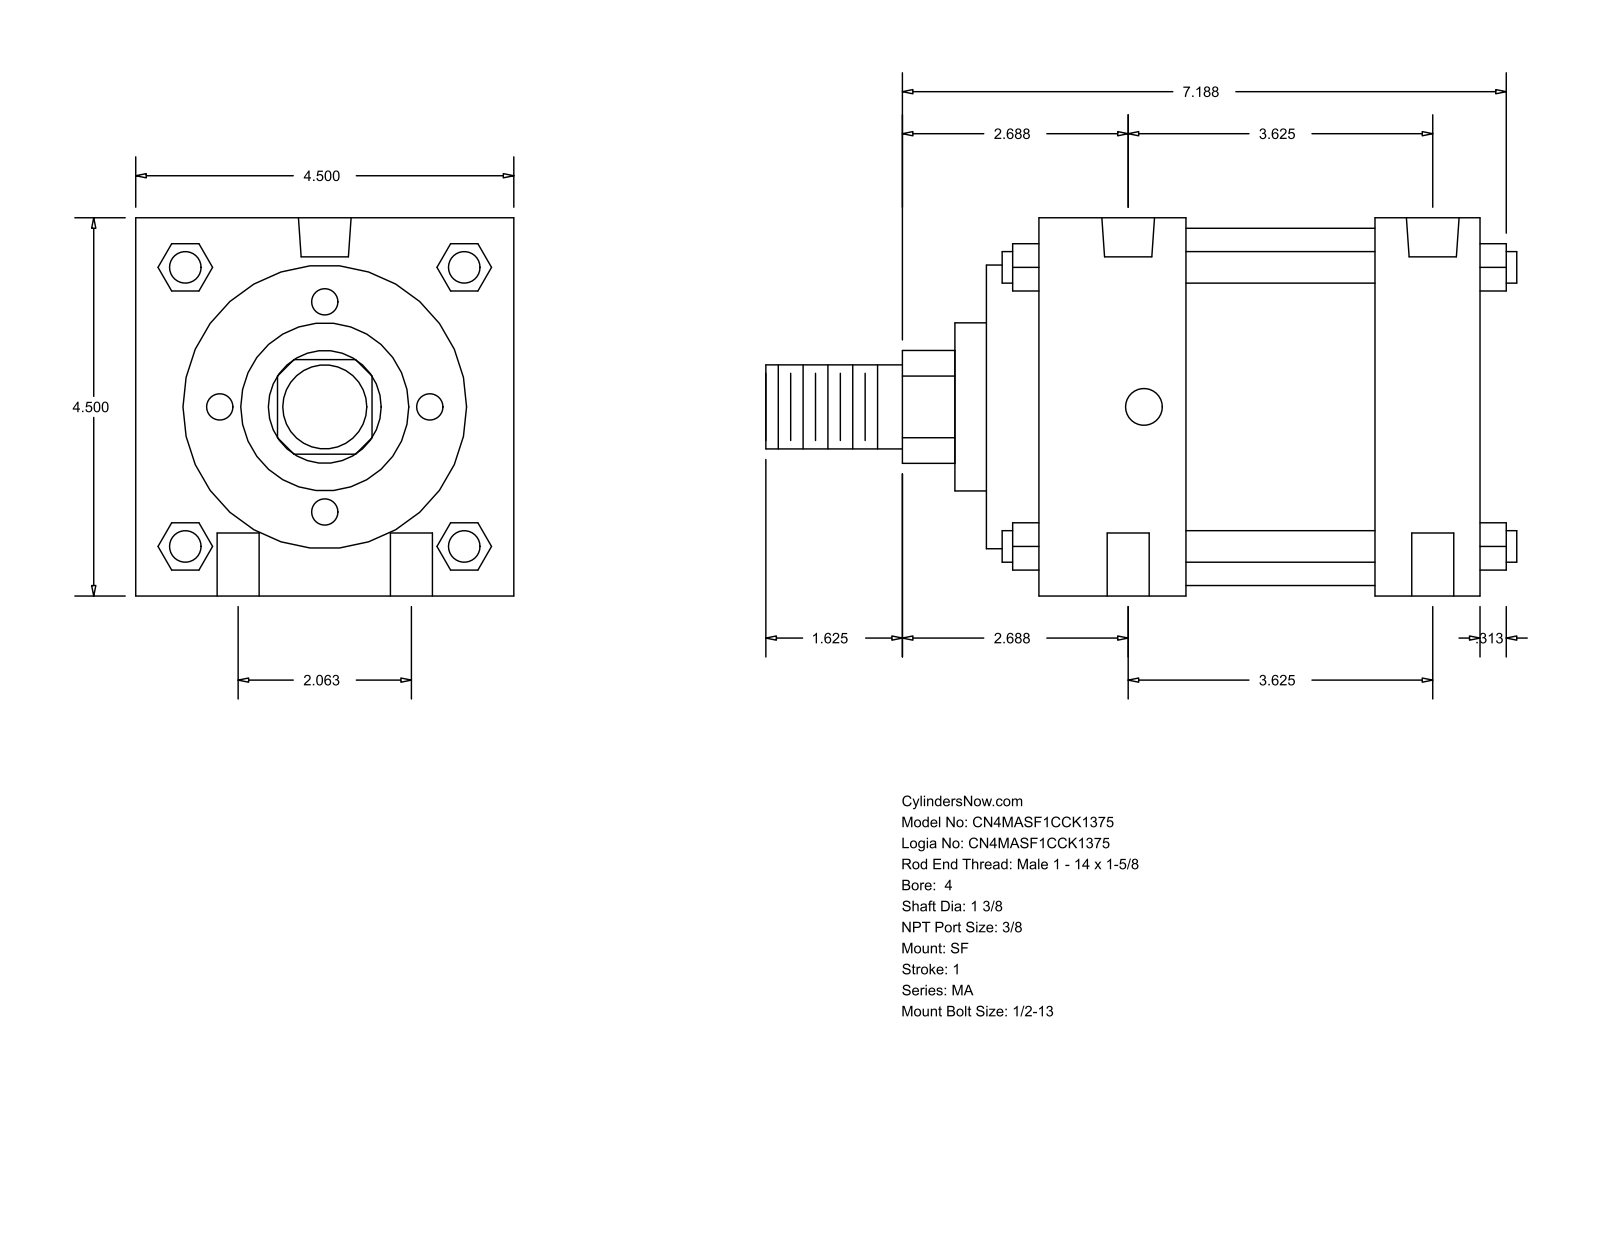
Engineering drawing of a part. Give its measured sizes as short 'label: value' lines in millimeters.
name: MA_SF__0400_1.375
written by: GSSL Pune (CONFIG_CONTROL_DESIGN)
unit: mm
bodies: 0 solids, 126 faces (95 planar, 31 cylindrical, 0 other)
size: 227.01 × 114.3 × 114.3
holes: 4× ⌀12.7, 2× ⌀11.11, 2× ⌀15.93
bosses: 4× ⌀9.53, 1× ⌀107.95, 1× ⌀85.72, 1× ⌀50.8, 1× ⌀34.92, 1× ⌀25.4
rounds: 1× R17.06
face distances: 114.3, 133.35, 149.22, 15.87, 117.48, 101.61, 31.74, 60.32, 44.45, 57.16
hole spacings: 26.19, 95.73, 92.08, 52.38, 105.94, 82.54
